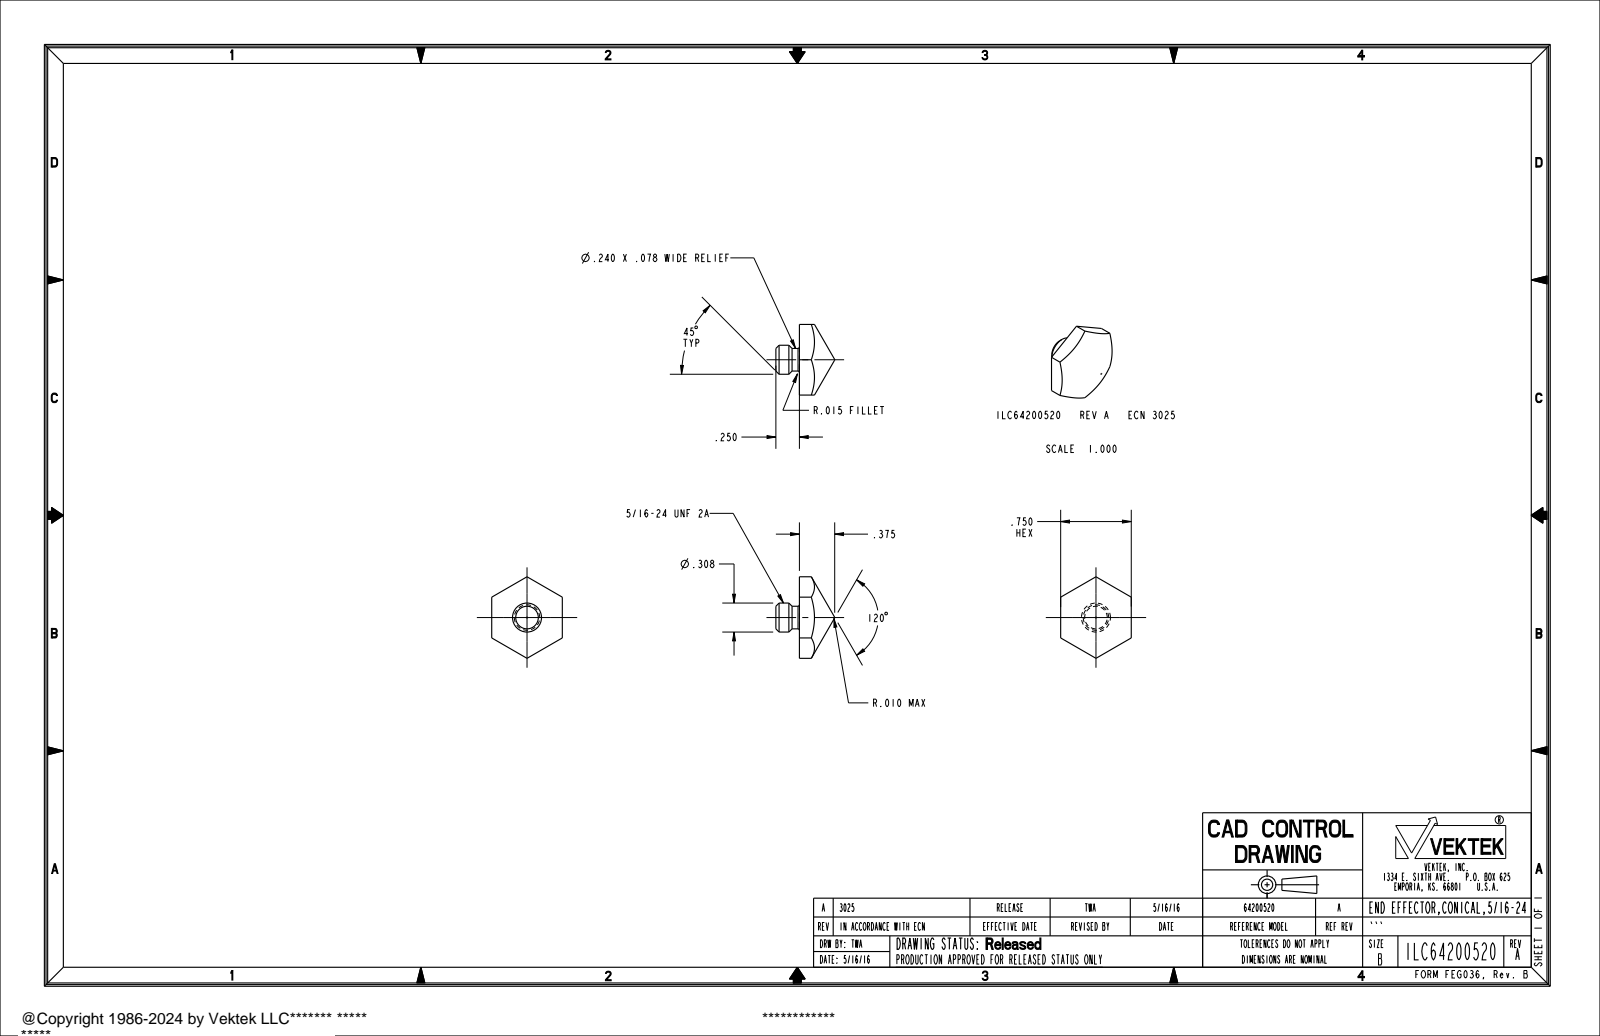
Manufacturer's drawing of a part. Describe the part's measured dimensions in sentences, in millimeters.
The part is named "ILC64200520". Its 3-D file was written by "PRO/ENGINEER BY PARAMETRIC TECHNOLOGY CORPORATION, 2013320 (CONFIG_CONTROL_DESIGN)". It is 1 solid with 22 faces: 8 planar, 4 cylindrical and 10 other. Overall it measures 22 by 19.1 by 15.9 millimeters. Its volume is 2 050 cubic millimeters and its surface area 1 079 square millimeters. Round bosses or shafts: 1 of diameter 7.8, 1 of diameter 6.1. The main face-to-face distances are 19.1, 6.4.
